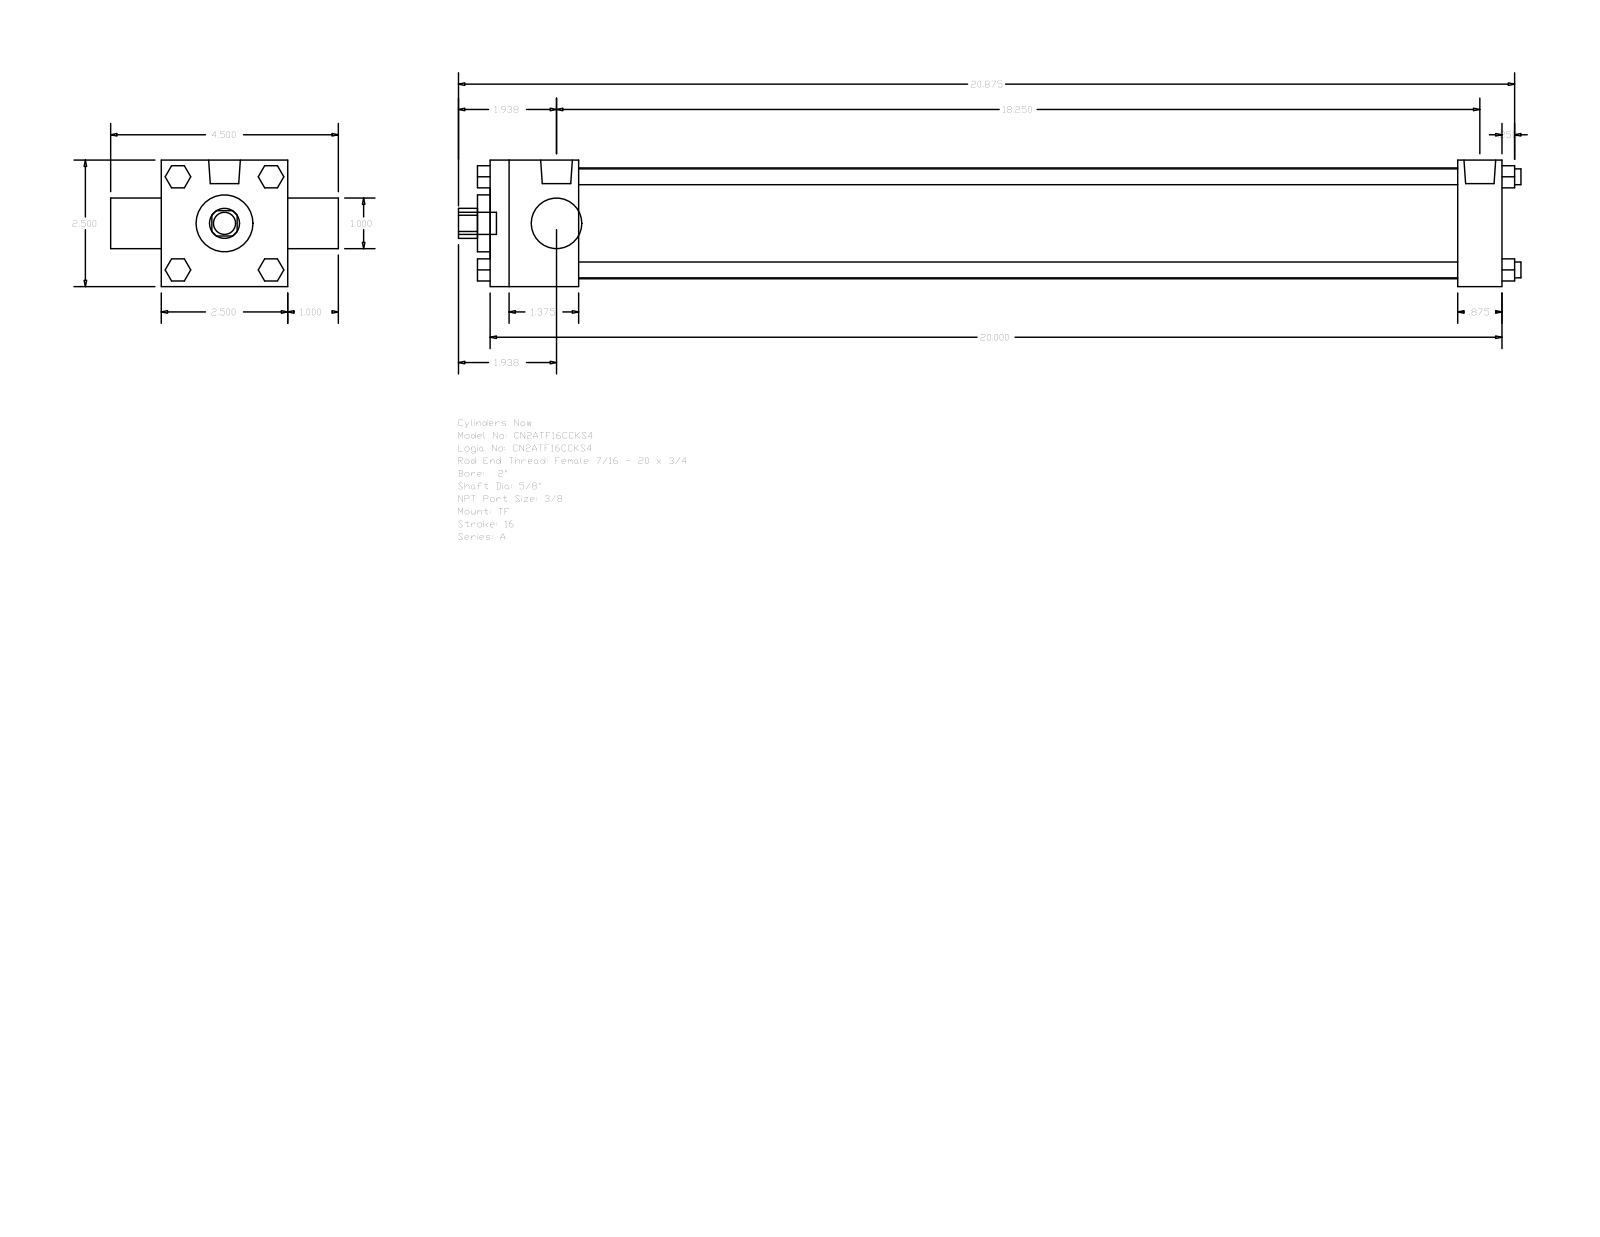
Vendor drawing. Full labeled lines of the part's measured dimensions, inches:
Part name (STEP PRODUCT): A_TF__0200_0.625
STEP written by: GSSL Pune (CONFIG_CONTROL_DESIGN)
Units: inches
Bodies: 0 solids, 120 faces (92 planar, 28 cylindrical, 0 other)
Overall size (bounding box): 21 × 4.5 × 2.5
Round holes (diameter × count): ⌀0.625 ×1, ⌀1 ×1, ⌀1.125 ×1, ⌀2.19 ×1
Round bosses / shafts (diameter × count): ⌀0.313 ×4, ⌀0.219 ×3, ⌀0.627 ×2, ⌀0.437 ×1
Partial cylindrical surfaces — rounded edges, fillets, slot ends (radius × count): R0.297 ×1
Main face-to-face distances: 2.5, 20, 1.75, 19.125, 17.375, 18.25, 0.875, 1, 3.5, 20.25
